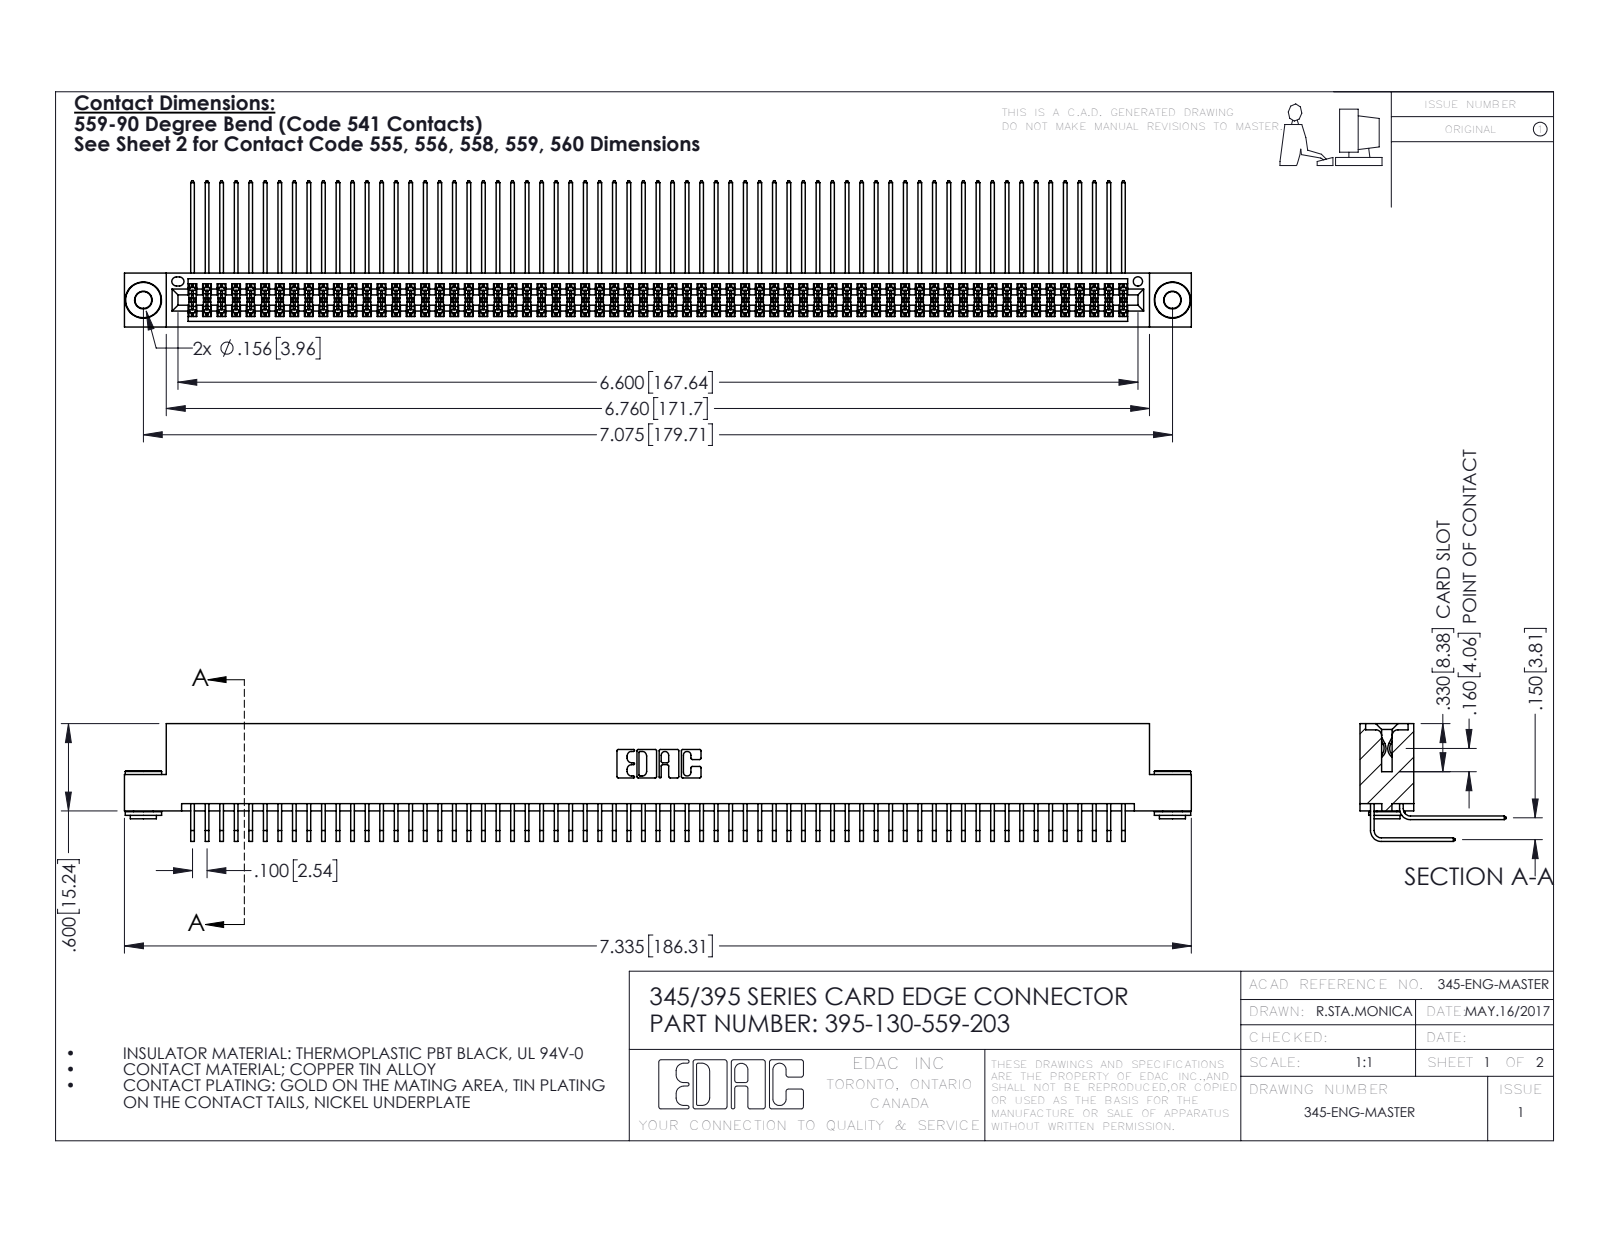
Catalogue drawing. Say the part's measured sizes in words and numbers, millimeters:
The part is named "345-292-001_558 559 Tail - 1; 395-130-559-203; 345-250-002_345-250-002-102; 345-292-001_559 Tail - 2 (+1 more)". Its 3-D file was written by "SolidWorks 2016 (CONFIG_CONTROL_DESIGN)". It is 133 solids with 6924 faces: 4640 planar, 2276 cylindrical and 8 other. Overall it measures 186.3 by 25.5 by 20.5 millimeters. Its volume is 19 070 cubic millimeters and its surface area 32 380 square millimeters. Round holes: 2 of diameter 2.9, 2 of diameter 4, 1 of diameter 1.6. Round bosses or shafts: 2 of diameter 6.4, 2 of diameter 4.6, 2 of diameter 3.5. Partial cylindrical surfaces (rounded edges, fillets, slot ends): 196 of radius 0.2, 22 of radius 0.3, 6 of radius 0.2, 6 of radius 0.8, 3 of radius 0.7, 2 of radius 0.4, 2 of radius 0.5, 2 of radius 0.6. The main face-to-face distances are 1.8, 7.6, 5.1, 9.4, 0.6, 2.5, 6.9, 5.7, 4.4, 3.8. The hole center spacings are 6.9, 173.7, 179.7.
